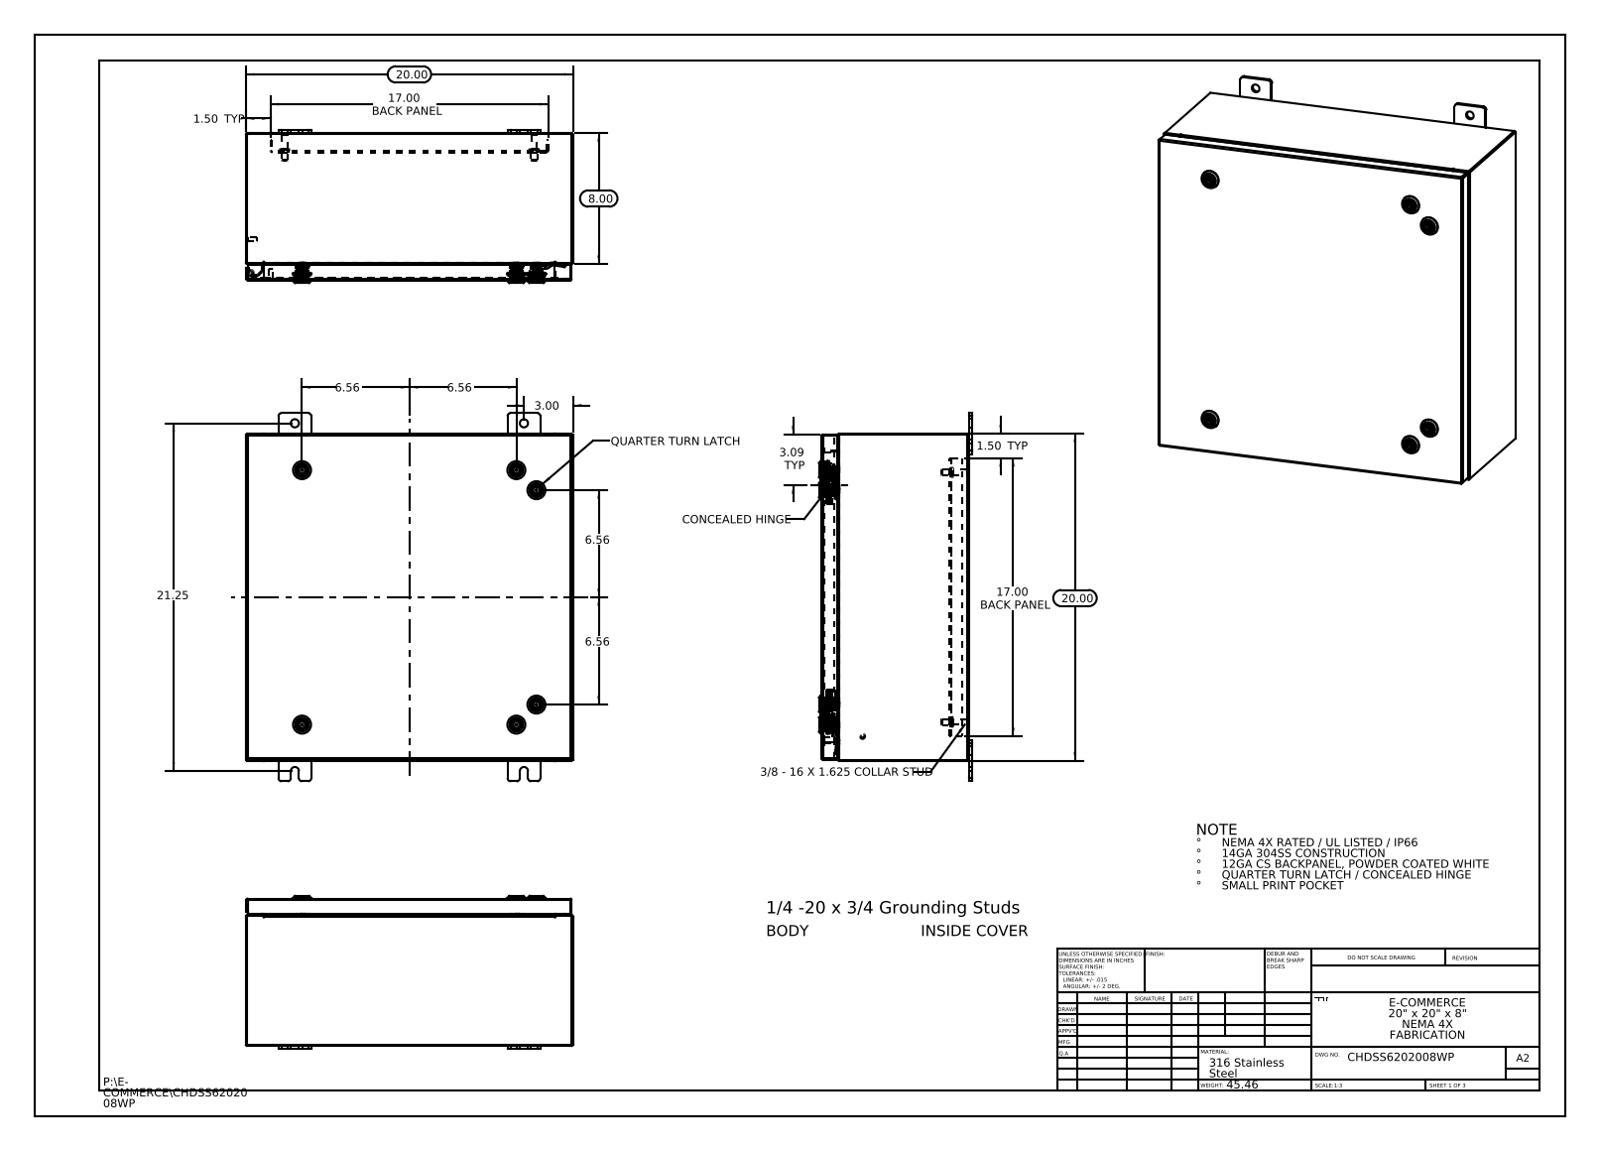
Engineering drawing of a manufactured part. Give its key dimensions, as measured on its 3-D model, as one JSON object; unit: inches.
{"part_name": "HW-CLH-E5-8004_Cam-232112-U-Industrilas; Screw-221320-IB-Industrilas_Screw-221320-IB-Industrilas; Housing-211301-IB-Industrilas_Housing-211301-IB-Industrilas; Quarter-20 CD Stud (+8 more)", "step_written_by": "SolidWorks 2013 (CONFIG_CONTROL_DESIGN)", "units": "inches", "bodies": {"solids": 55, "faces": 5420, "planar": 1592, "cylindrical": 1692, "other": 2136}, "overall_size": [22.5, 20, 9.356], "volume_in3": 163.2, "surface_area_in2": 4087, "round_holes": [[0.5, 8], [0.197, 6], [0.394, 6], [0.4, 6], [0.63, 6], [0.787, 6], [0.136, 4], [0.211, 1]], "round_bosses_or_shafts": [[0.236, 8], [1.102, 6], [0.78, 6], [0.626, 6], [0.61, 6], [0.531, 6], [0.392, 6], [0.114, 6]], "partial_cylinders_radius": [[0.006, 198], [0.118, 198], [0.028, 72], [0.02, 24], [0.19, 24], [0.197, 24], [0.013, 20], [0.088, 18]], "face_to_face_distances": [0.075, 19.925, 0.074, 9.01, 8.935, 8.936, 8.861, 19.85, 20, 0.104], "hole_center_spacings": [13.1, 14.378, 0.688, 1.858, 3.065, 13.687, 14, 14.164]}
